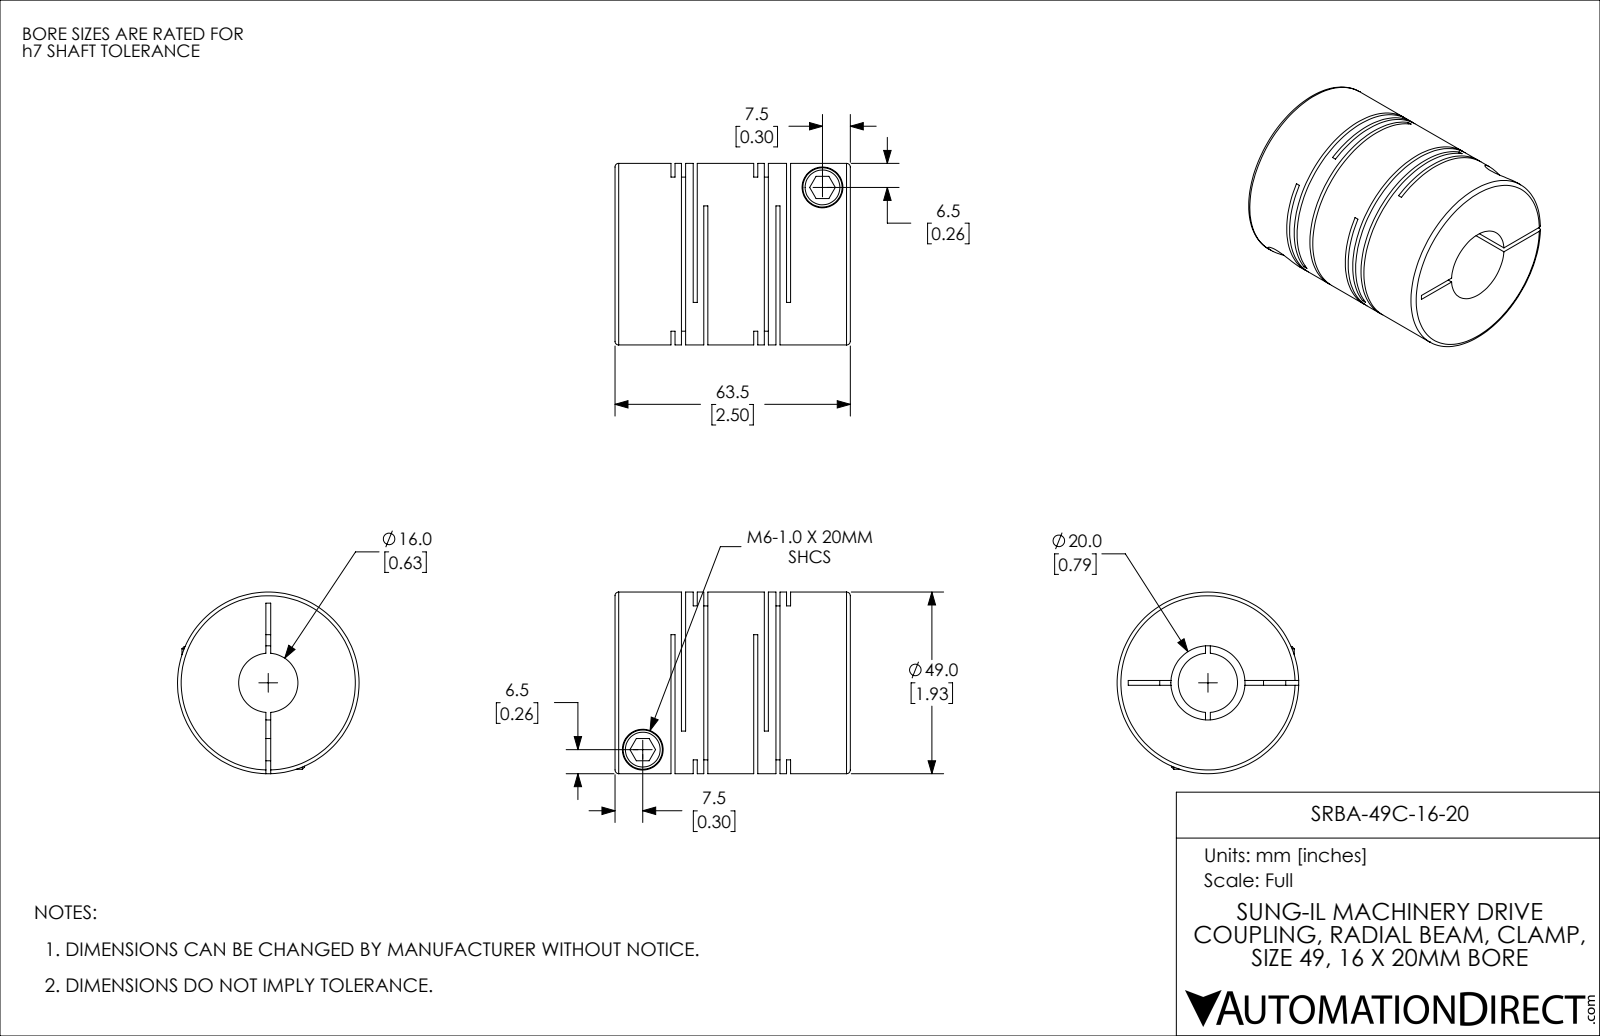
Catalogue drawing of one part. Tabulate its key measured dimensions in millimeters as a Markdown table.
| quantity | value |
| --- | --- |
| part name | SRBA-49C-16-20 |
| STEP written by | SolidWorks 2021 (CONFIG_CONTROL_DESIGN) |
| units | millimeters |
| bodies | 1 solid, 114 faces (60 planar, 42 cylindrical, 12 other) |
| overall size | 63.5 × 49 × 49 |
| volume | 87 859 mm³ |
| surface area | 38 116 mm² |
| round holes (diameter × count) | 6 × 2, 11 × 2, 16 × 1, 20 × 1 |
| round bosses / shafts (diameter × count) | 10.6 × 2, 49 × 1 |
| main face-to-face distances | 6, 1.1, 2.85, 22.35, 1.75, 4.9, 21.25, 3.15, 19.5, 16.35 |
